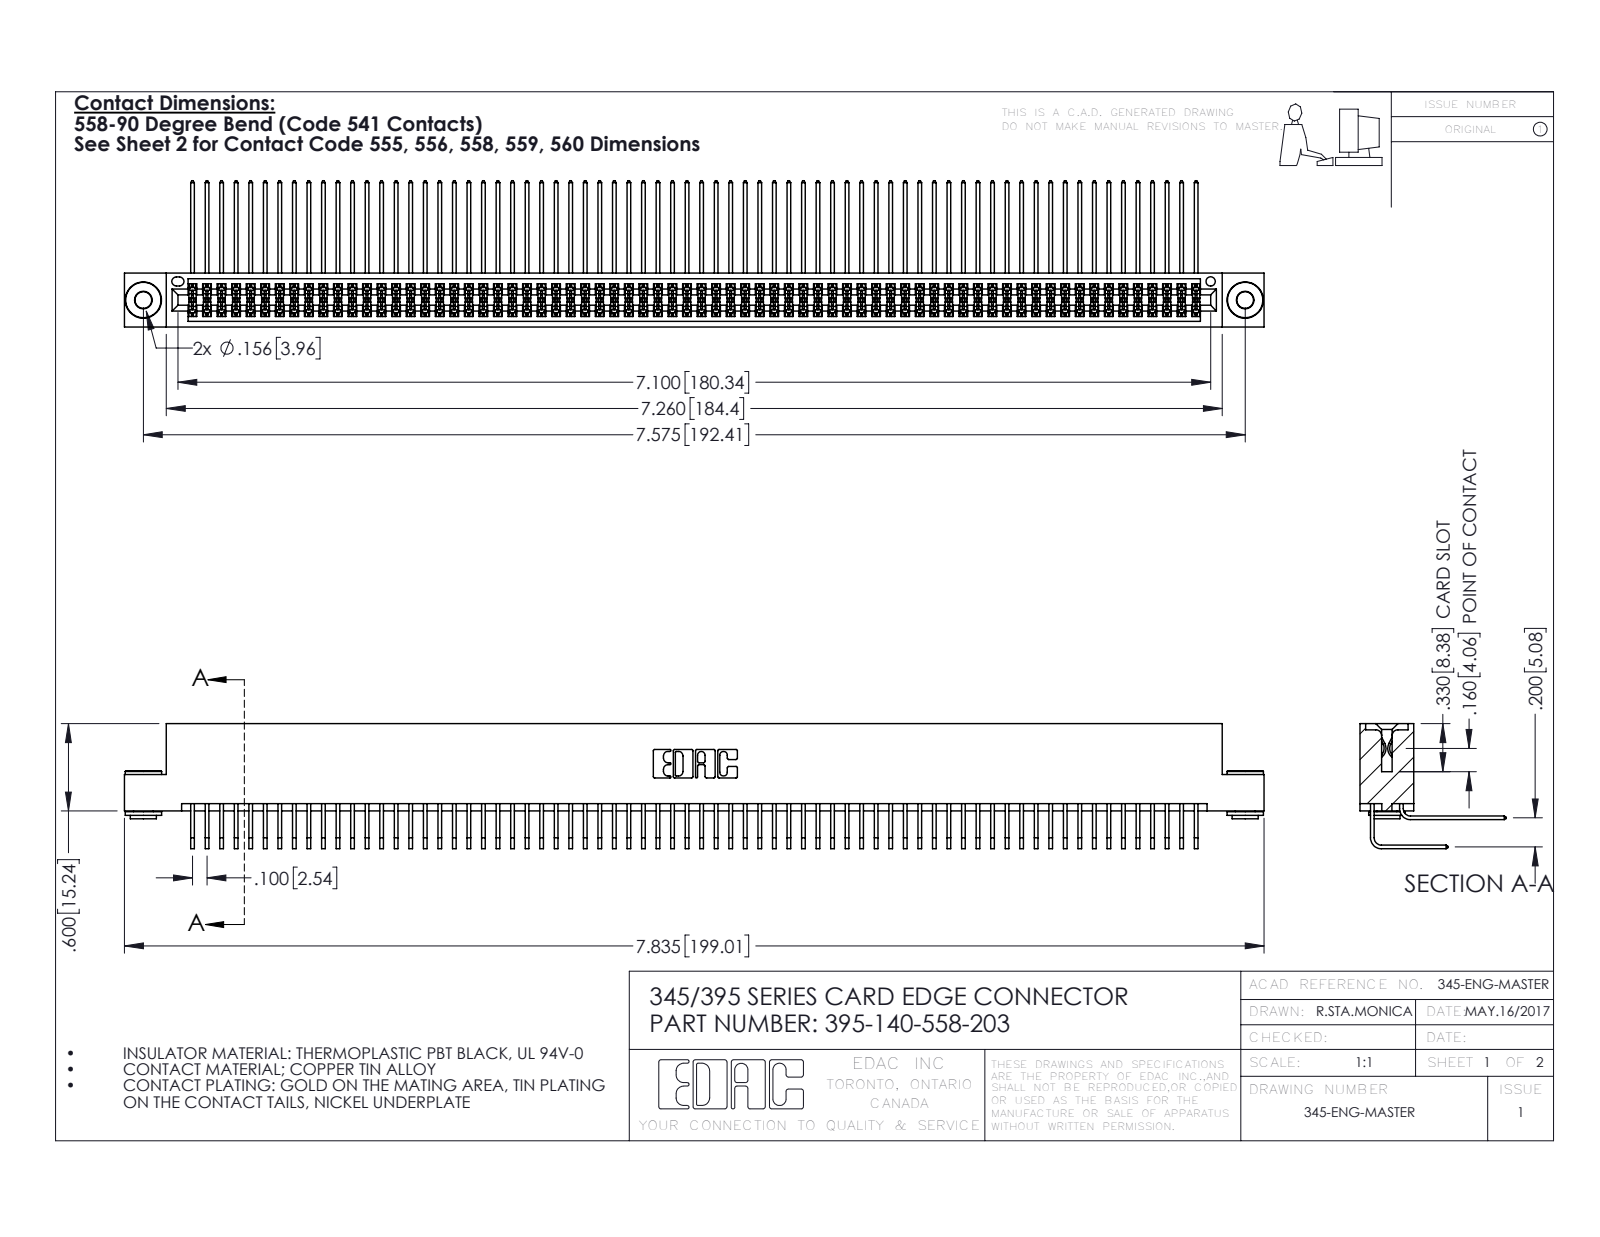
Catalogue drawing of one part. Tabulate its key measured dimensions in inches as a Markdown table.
| quantity | value |
| --- | --- |
| part name | 345-292-001_558 Tail - 2; 395-140-558-203; 345-292-001_558 559 Tail - 1; 345 Part_Flush Mounting Lugs - 0.156 Dia-TH (+1 more) |
| STEP written by | SolidWorks 2016 (CONFIG_CONTROL_DESIGN) |
| units | inches |
| bodies | 143 solids, 7444 faces (4990 planar, 2446 cylindrical, 8 other) |
| overall size | 7.835 × 1.005 × 0.859 |
| volume | 1.246 in³ |
| surface area | 53.83 in² |
| round holes (diameter × count) | 0.116 × 2, 0.156 × 2, 0.064 × 1 |
| round bosses / shafts (diameter × count) | 0.25 × 2, 0.18 × 2, 0.136 × 2 |
| partial cylindrical surfaces (radius × count) | 0.006 × 279, 0.01 × 22, 0.007 × 6, 0.031 × 6, 0.026 × 3, 0.014 × 2, 0.019 × 2, 0.022 × 2 |
| main face-to-face distances | 0.072, 0.298, 0.2, 0.37, 0.025, 0.098, 0.272, 0.225, 0.025, 0.175 |
| hole center spacings | 0.27, 7.339, 7.575 |
